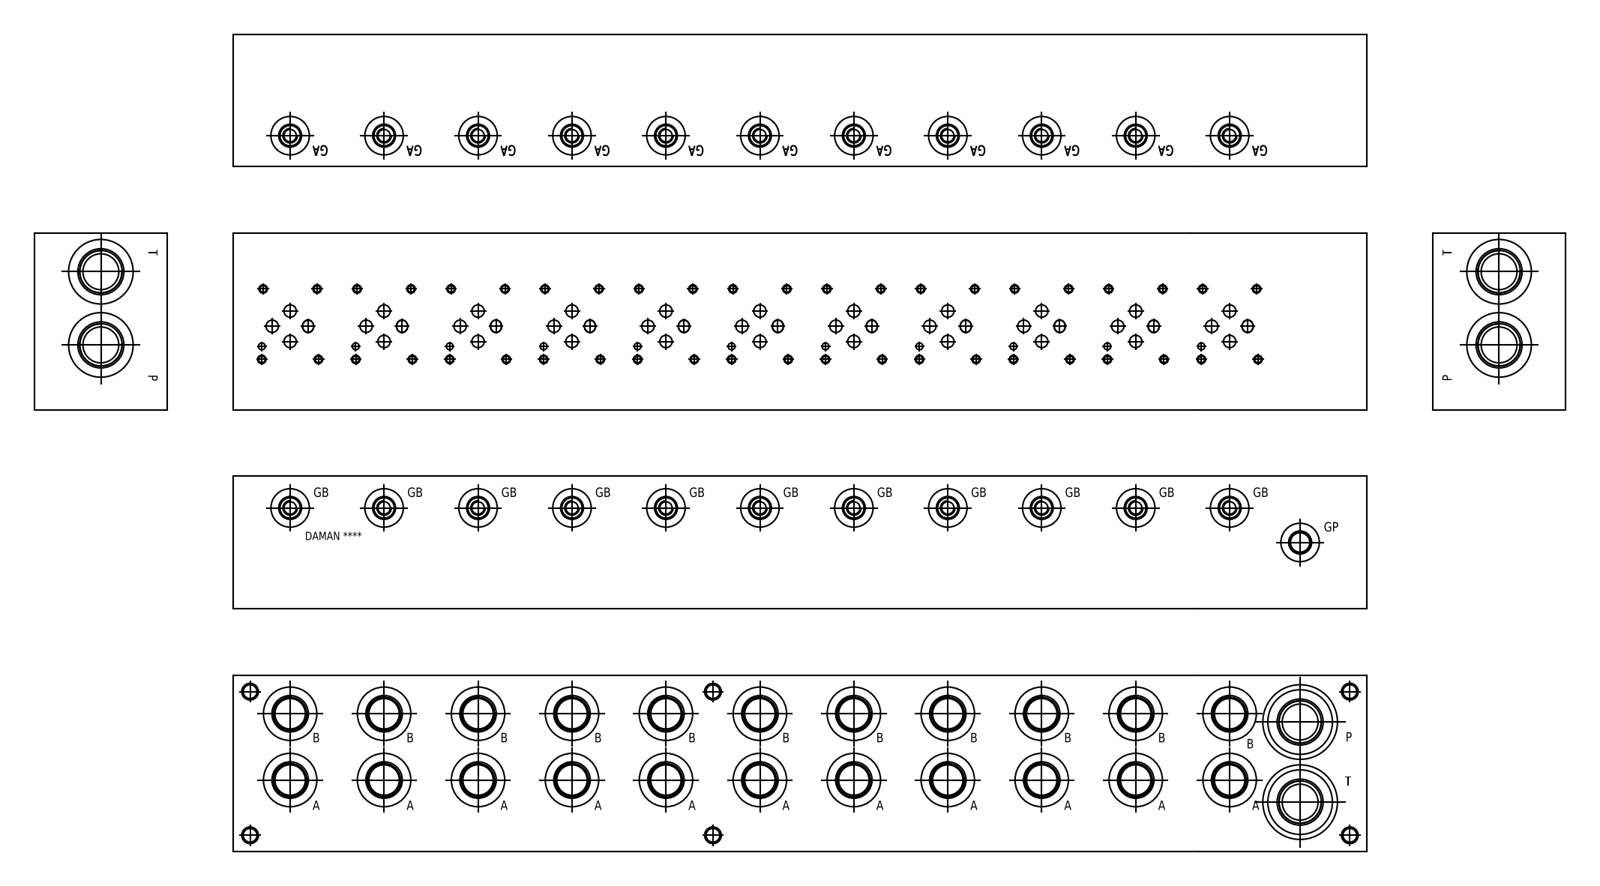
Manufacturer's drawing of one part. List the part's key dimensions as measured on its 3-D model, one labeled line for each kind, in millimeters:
Part name (STEP PRODUCT): Part_AD03PB112B_3D
STEP written by: Autodesk Inventor 2019 (AUTOMOTIVE_DESIGN)
Units: millimetres
Bodies: 1 solid, 2541 faces (1221 planar, 358 cylindrical, 962 other)
Overall size (bounding box): 650.88 × 101.6 × 76.2
Volume: 4 652 000 mm³ · Surface area: 335 381 mm²
Round holes (diameter × count): ⌀7.14 ×55, ⌀4.22 ×44, ⌀5 ×44, ⌀11.68 ×23, ⌀13.26 ×23, ⌀22.12 ×23, ⌀17.48 ×22, ⌀21.06 ×22, ⌀30.68 ×22, ⌀18.92 ×12, ⌀3.96 ×11, ⌀6.35 ×11
Main face-to-face distances: 76.2, 101.6, 0.79, 75.41, 100.81, 650.88, 100.02, 650.09, 17.37, 16.58
Hole centre spacings: 107.95, 215.9, 53.97, 53.98, 323.85, 161.92, 161.93, 114.48
